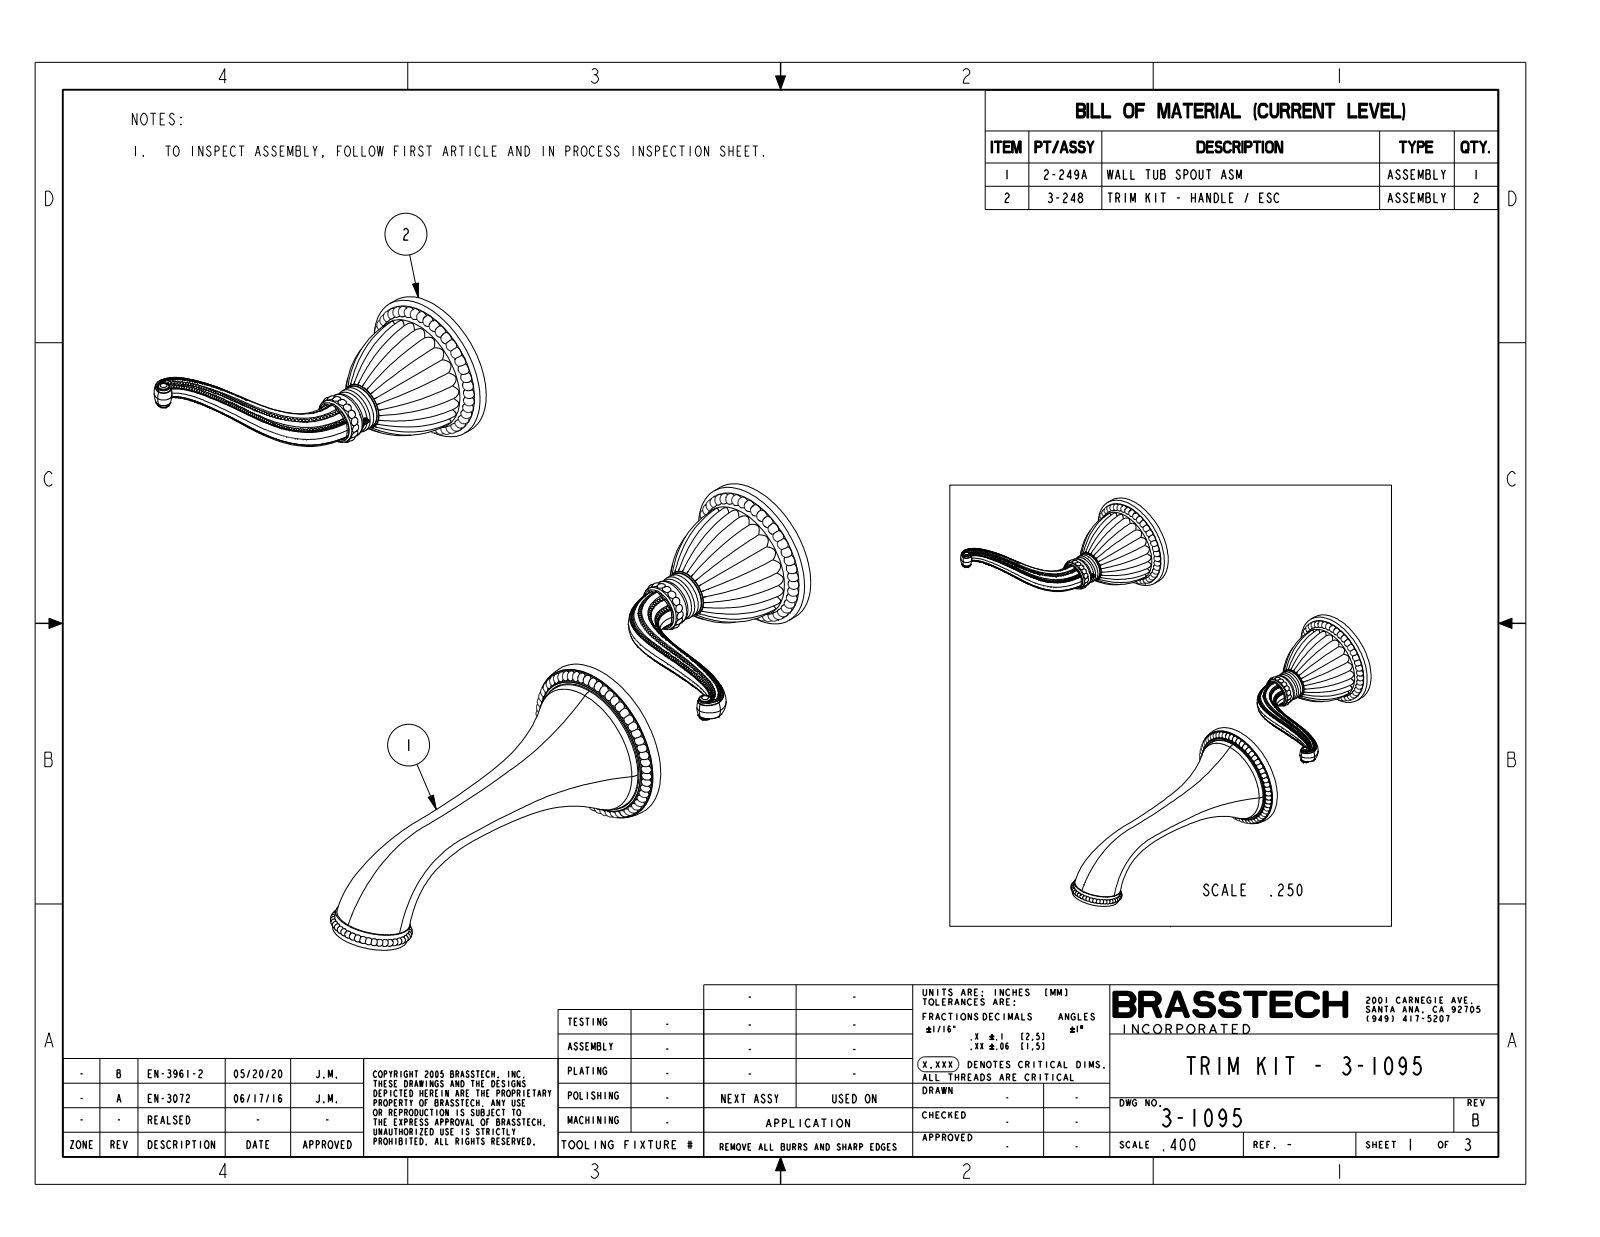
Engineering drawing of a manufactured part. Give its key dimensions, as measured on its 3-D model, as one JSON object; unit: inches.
{"part_name": "3-1095_SW0001", "step_written_by": "CREO PARAMETRIC BY PTC INC, 2018400 (AUTOMOTIVE_DESIGN)", "units": "inches", "bodies": {"solids": 5, "faces": 6558, "planar": 752, "cylindrical": 2210, "other": 3596}, "overall_size": [13.643, 8.71, 6.293], "volume_in3": 19.26, "surface_area_in2": 96.12, "round_holes": [[0.04, 378], [0.05, 97], [0.045, 46], [0.041, 22]], "round_bosses_or_shafts": [[2.57, 2], [0.79, 2], [0.775, 2], [0.532, 2], [2.435, 1], [2.345, 1], [1.3, 1], [1.102, 1]], "face_to_face_distances": [0.16, 2, 1.84, 0.29, 0.13, 1.71, 1.97, 1.81, 1.68, 0.03], "hole_center_spacings": [0.239, 0.05, 0.05, 0.05, 0.061, 0.102, 0.144, 0.157]}
